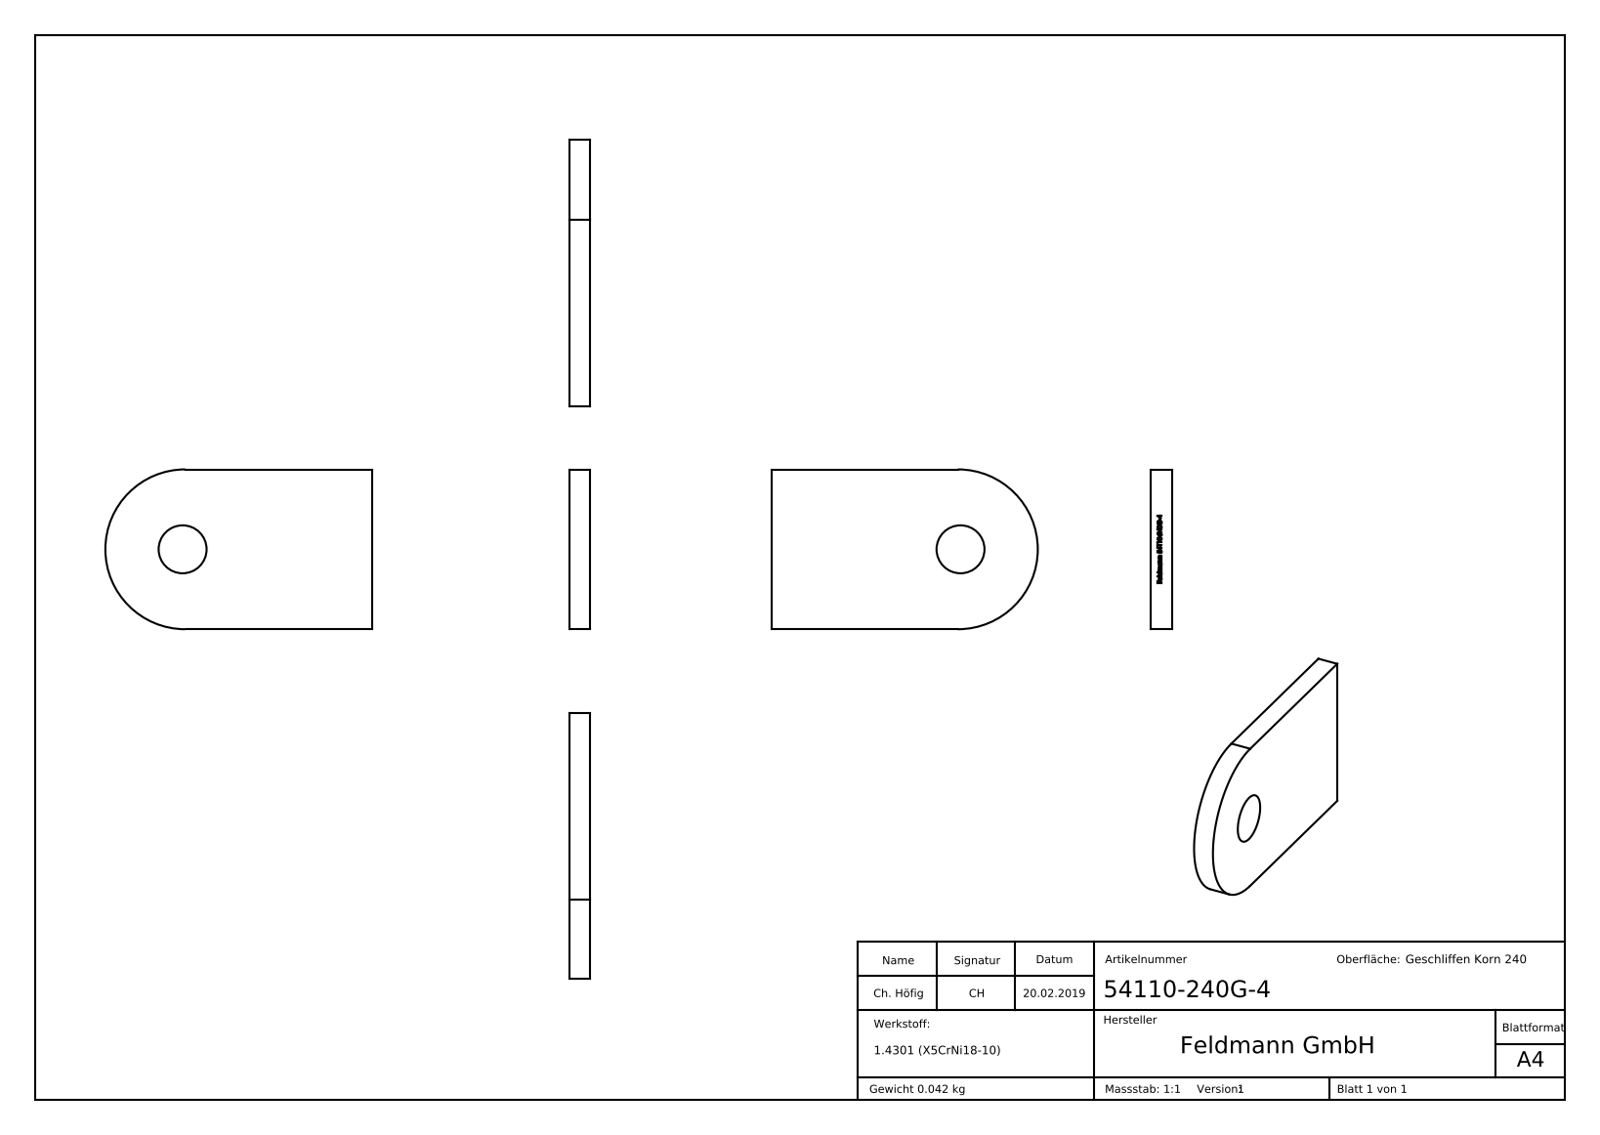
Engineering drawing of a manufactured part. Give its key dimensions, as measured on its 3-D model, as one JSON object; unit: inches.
{"part_name": "54110-240G-4", "step_written_by": "SolidWorks 2015 (CONFIG_CONTROL_DESIGN)", "units": "inches", "bodies": {"solids": 1, "faces": 255, "planar": 162, "cylindrical": 4, "other": 89}, "overall_size": [1.969, 1.181, 0.157], "volume_in3": 0.327, "surface_area_in2": 5.251, "round_holes": [[0.354, 1]], "partial_cylinders_radius": [[0.591, 1]], "face_to_face_distances": [0.157, 1.181, 0.079, 0.024, 0.048, 0.089, 0.021, 0.111, 0.069, 0.017]}
